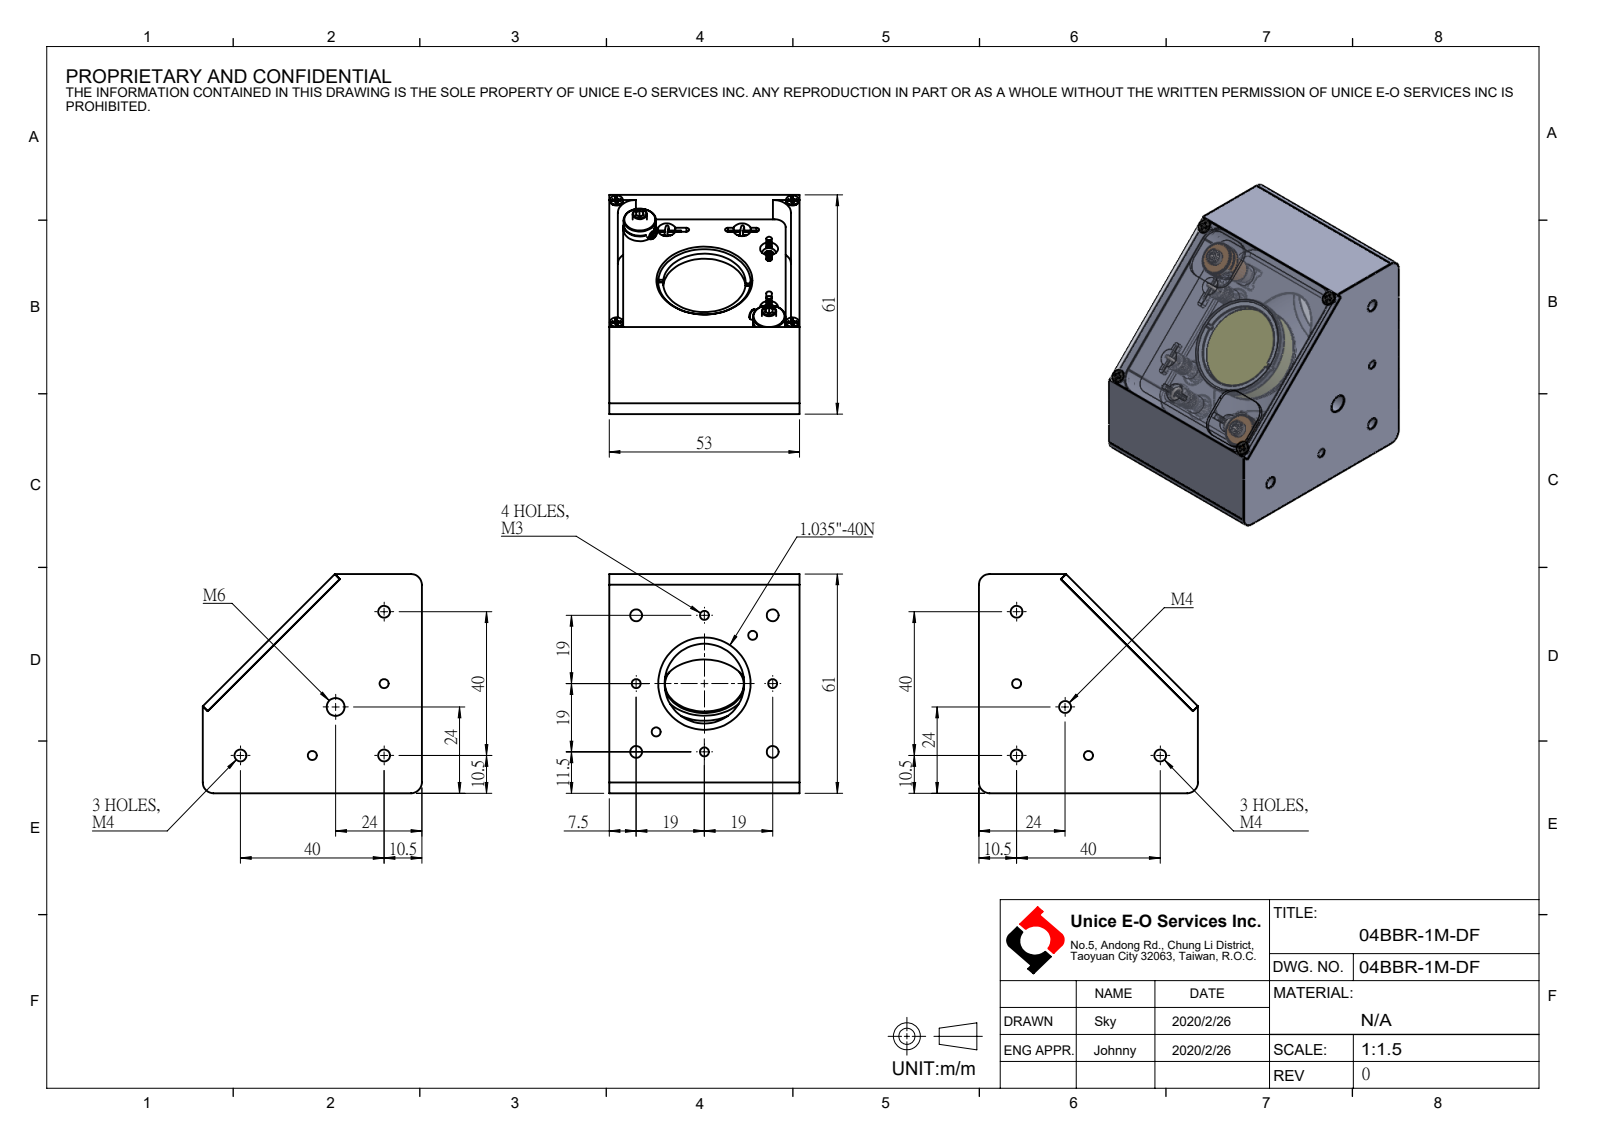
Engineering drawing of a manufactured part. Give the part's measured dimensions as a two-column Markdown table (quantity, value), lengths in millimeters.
| quantity | value |
| --- | --- |
| part name | 04BBR-1M-DF |
| STEP written by | SolidWorks 2016 (CONFIG_CONTROL_DESIGN) |
| units | millimeters |
| bodies | 0 solids, 161 faces (54 planar, 87 cylindrical, 20 other) |
| overall size | 61 × 61 × 53 |
| round holes (diameter × count) | 2.5 × 14, 3.3 × 12, 22.2 × 2, 25.7 × 2, 27.1 × 2, 5 × 1 |
| round bosses / shafts (diameter × count) | 3.6 × 4 |
| partial cylindrical surfaces (radius × count) | 3 × 3 |
| main face-to-face distances | 53, 61, 19.7, 3.8, 57.2, 19.3, 0.4, 1.67, 1.66, 48.86 |
| hole center spacings | 19, 26.87, 42.49, 38, 14.54, 32.91, 35.11, 7.86 |
